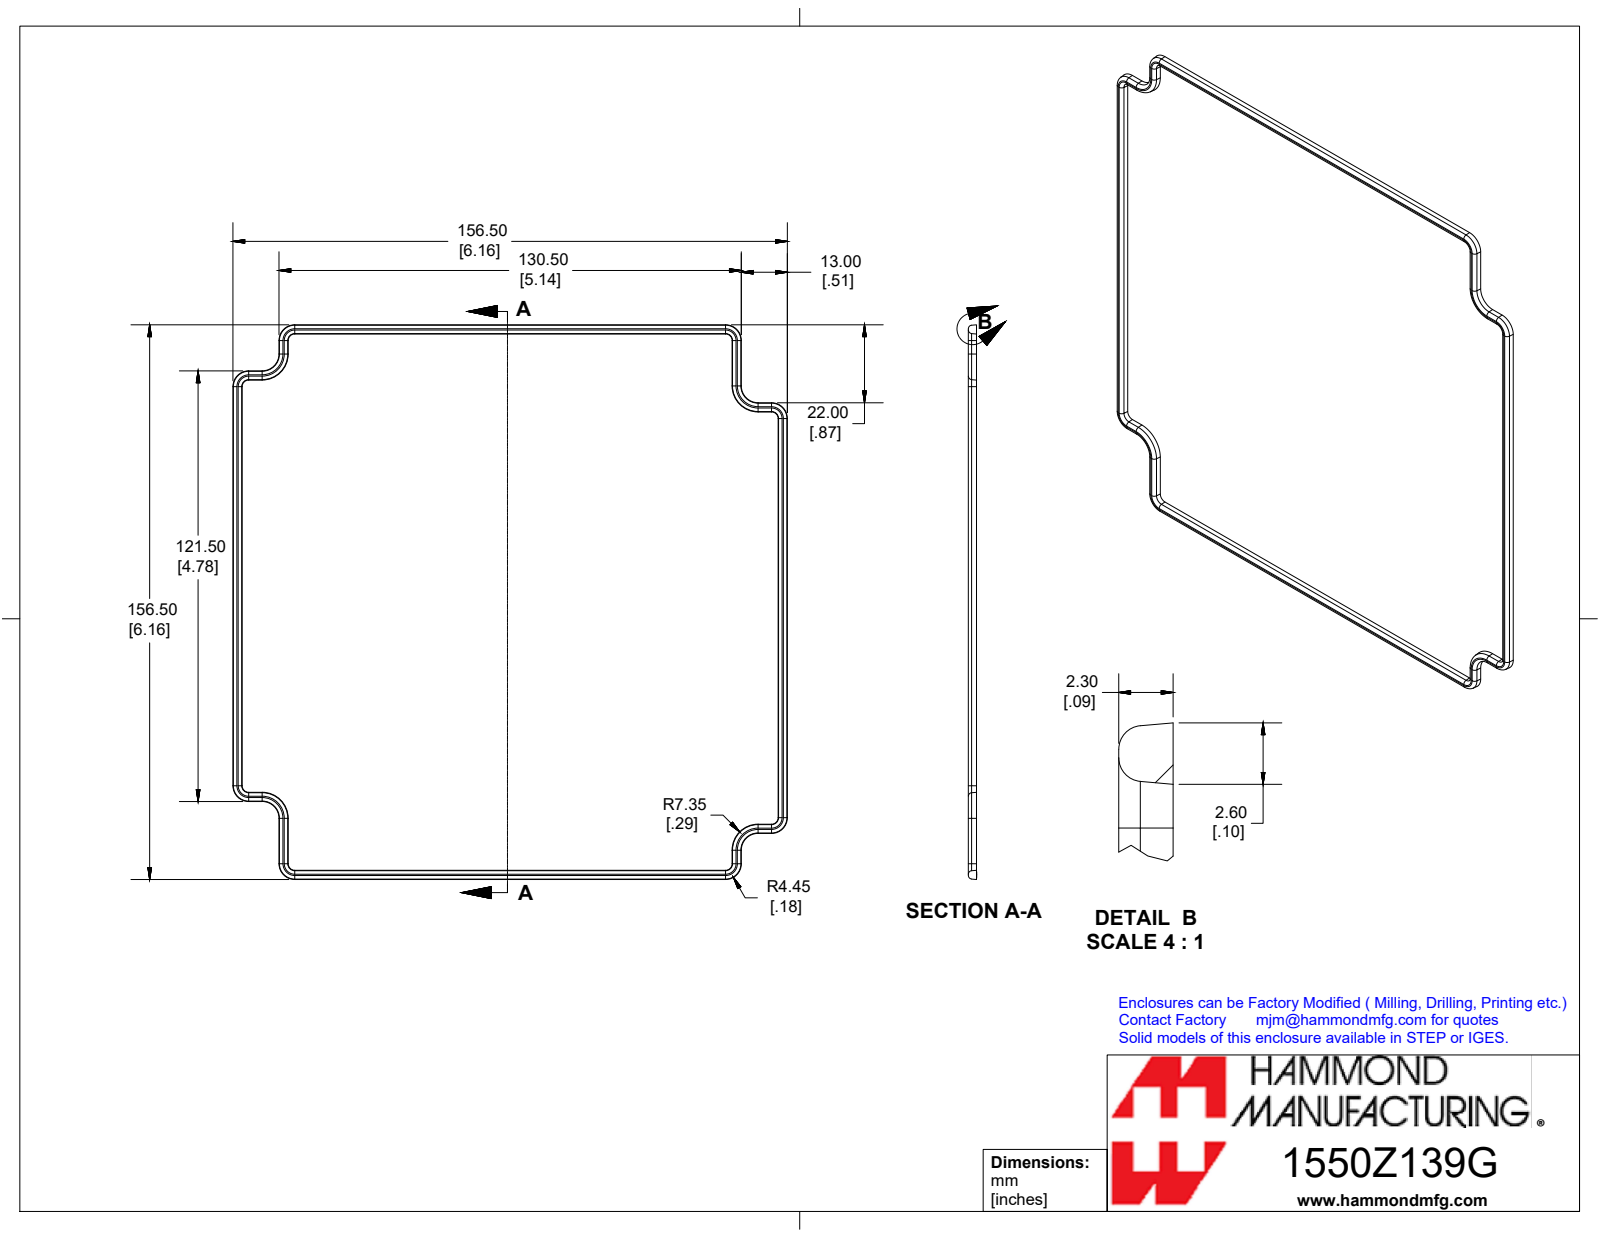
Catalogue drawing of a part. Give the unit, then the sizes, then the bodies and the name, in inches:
Units: inches
Overall size (bounding box): 6.161 × 6.161 × 0.093
Partial cylindrical surfaces — rounded edges, fillets, slot ends (radius × count): R0.039 ×20
Main face-to-face distances: 6.035, 0.091, 5.525, 0.51, 5.015, 5.172, 4.663, 0.353, 0.863, 0.863
Volume: 0.187 in³ · Surface area: 8.033 in²
Bodies: 1 solid, 161 faces (40 planar, 24 cylindrical, 97 other)
Part name (STEP PRODUCT): 1550Z139GASKET
STEP written by: SolidWorks 2019 (CONFIG_CONTROL_DESIGN)
